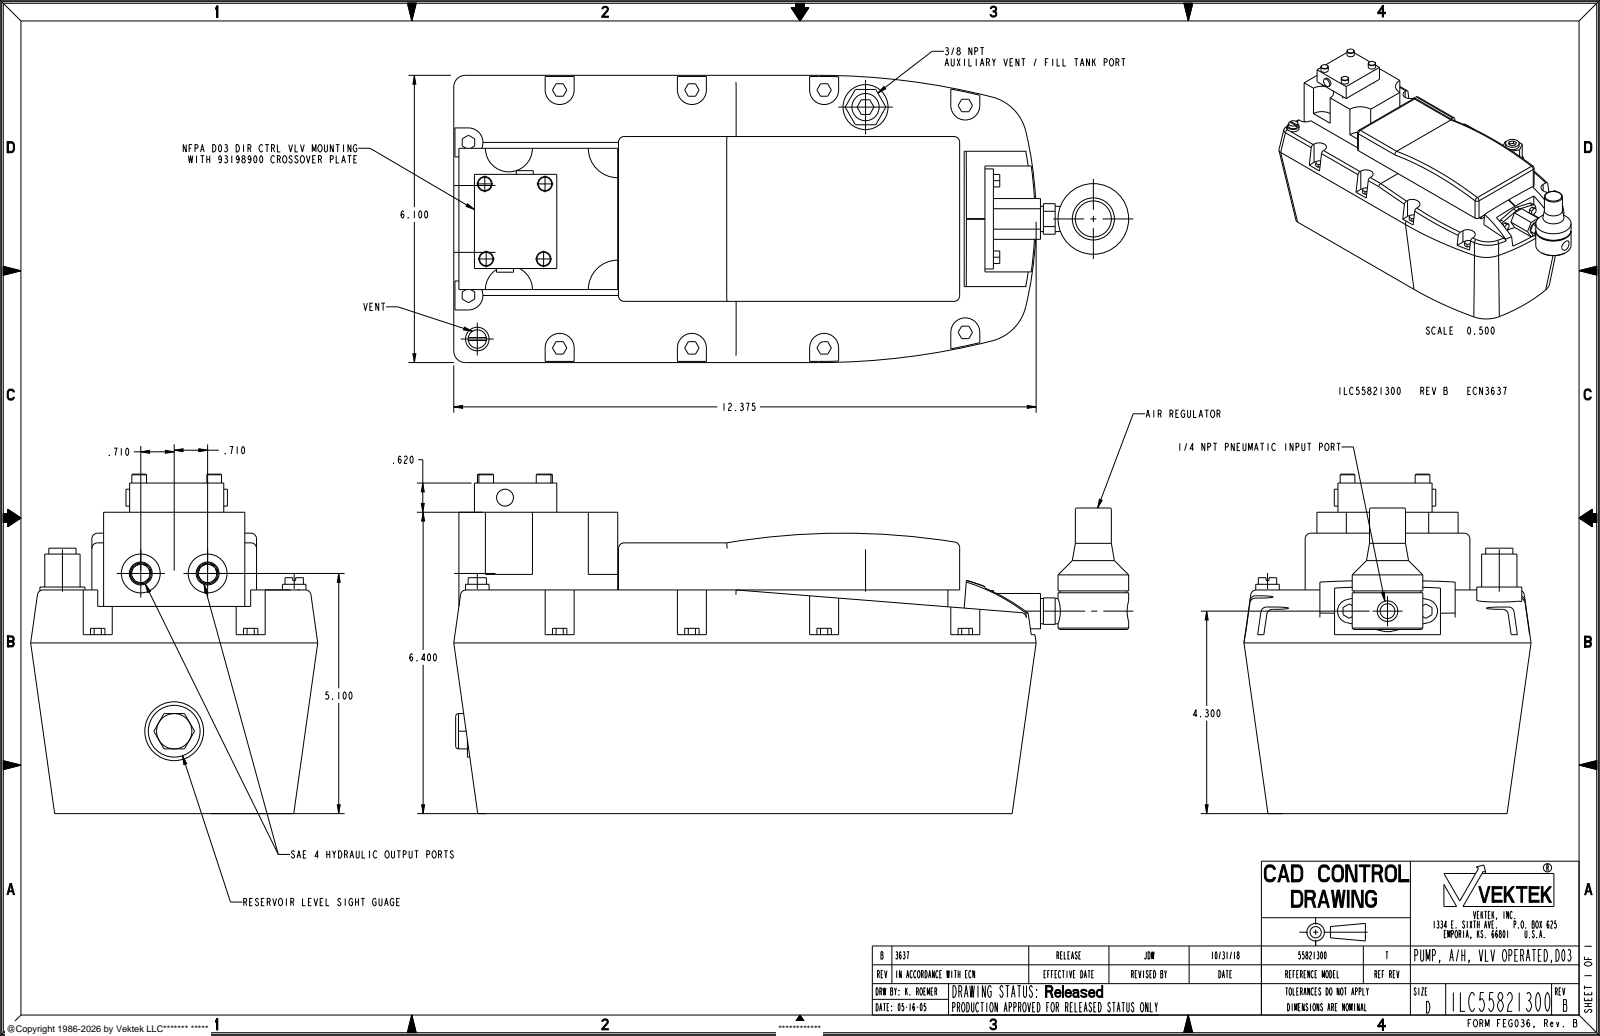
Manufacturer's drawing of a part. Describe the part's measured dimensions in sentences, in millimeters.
The part is named "ILC55821300; ILC55821300_CROSSOVER". Its 3-D file was written by "PRO/ENGINEER BY PARAMETRIC TECHNOLOGY CORPORATION, 2013320 (AUTOMOTIVE_DESIGN)". It is 6 solids with 511 faces: 268 planar, 155 cylindrical and 88 other. Overall it measures 364.3 by 183.1 by 154.9 millimeters. Its volume is 5 729 000 cubic millimeters and its surface area 261 700 square millimeters. Round holes: 7 of diameter 6.4, 4 of diameter 4, 4 of diameter 5.6, 4 of diameter 8.9, 2 of diameter 10, 2 of diameter 21, 1 of diameter 3.3, 1 of diameter 4.1, 1 of diameter 8, 1 of diameter 11.1, 1 of diameter 14.7, 1 of diameter 31.8. Round bosses or shafts: 4 of diameter 7.9, 4 of diameter 4.8, 2 of diameter 11.1, 2 of diameter 9.1, 1 of diameter 38.1, 1 of diameter 36.1, 1 of diameter 27.9, 1 of diameter 24.3. Partial cylindrical surfaces (rounded edges, fillets, slot ends): 14 of radius 3, 10 of radius 7.8, 6 of radius 6.4, 2 of radius 12.7, 2 of radius 15.9, 1 of radius 11.1, 1 of radius 381. The main face-to-face distances are 120.7, 153.4, 6.4, 162.6, 41.9, 82.6, 25.4, 88.9, 146.1, 16.5. The hole center spacings are 19.8, 22.2, 27.2, 32.7, 33.7, 34, 40.5, 51.5.
